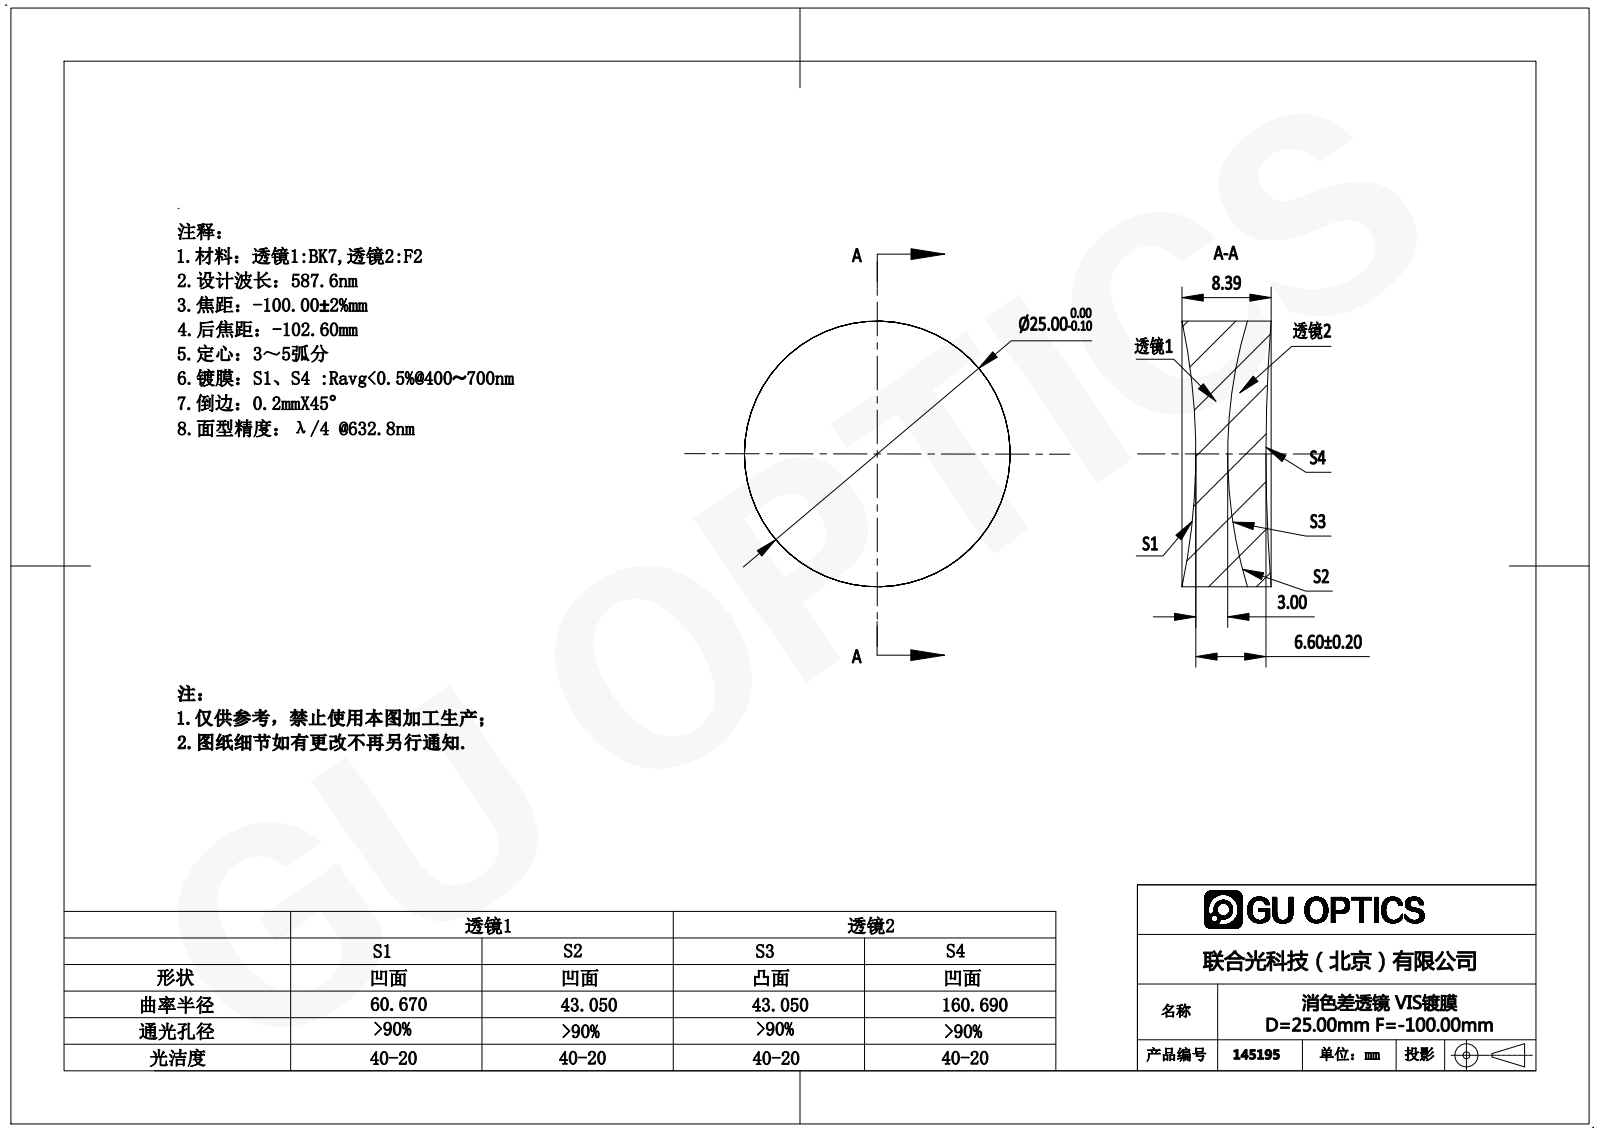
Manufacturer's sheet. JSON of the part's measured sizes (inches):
{"part_name": "145195", "step_written_by": "SolidWorks 2016 (AUTOMOTIVE_DESIGN)", "units": "inches", "bodies": {"solids": 2, "faces": 12, "planar": 0, "cylindrical": 4, "other": 8}, "overall_size": [0.984, 0.984, 0.33], "volume_in3": 0.224, "surface_area_in2": 4.108, "round_bosses_or_shafts": [[0.984, 1]]}
